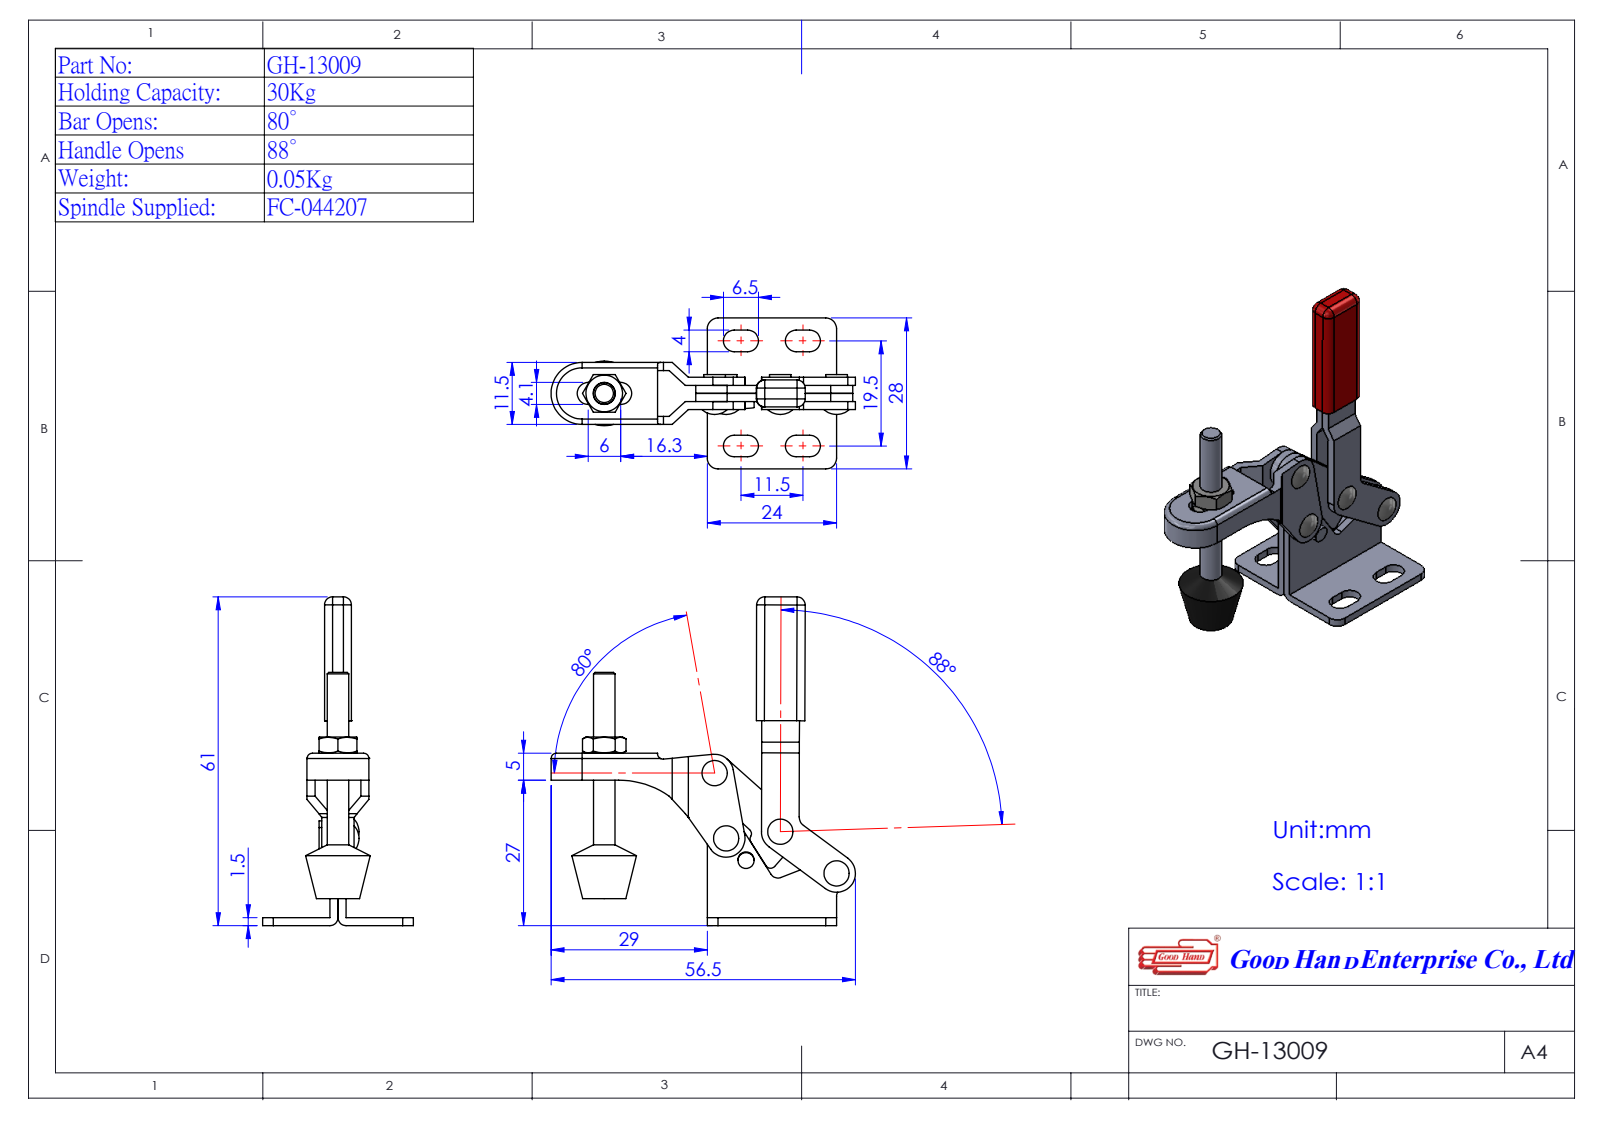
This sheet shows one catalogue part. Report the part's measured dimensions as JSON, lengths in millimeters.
{"part_name": "Group5^GH-13009(簡化)-1; Group4^GH-13009(簡化)-1; Group3^GH-13009(簡化)-1; Group2^GH-13009(簡化)-1 (+2 more)", "step_written_by": "SolidWorks 2016 (AUTOMOTIVE_DESIGN)", "units": "millimeters", "bodies": {"solids": 5, "faces": 219, "planar": 109, "cylindrical": 86, "other": 24}, "overall_size": [61.02, 56.5, 28], "volume_mm3": 6631, "surface_area_mm2": 7543, "round_holes": [[2.5, 4]], "round_bosses_or_shafts": [[4, 5], [7, 1], [2.5, 1]], "partial_cylinders_radius": [[2, 13], [1, 4], [3.5, 3], [1.5, 2], [2.05, 2], [3, 1], [4.25, 1], [5.75, 1]], "face_to_face_distances": [1.5, 3, 4.5, 0.5, 1, 4, 5.5, 6, 5, 2.75], "hole_center_spacings": [10.12, 12.26, 13, 16.19, 21.51, 29.15]}
